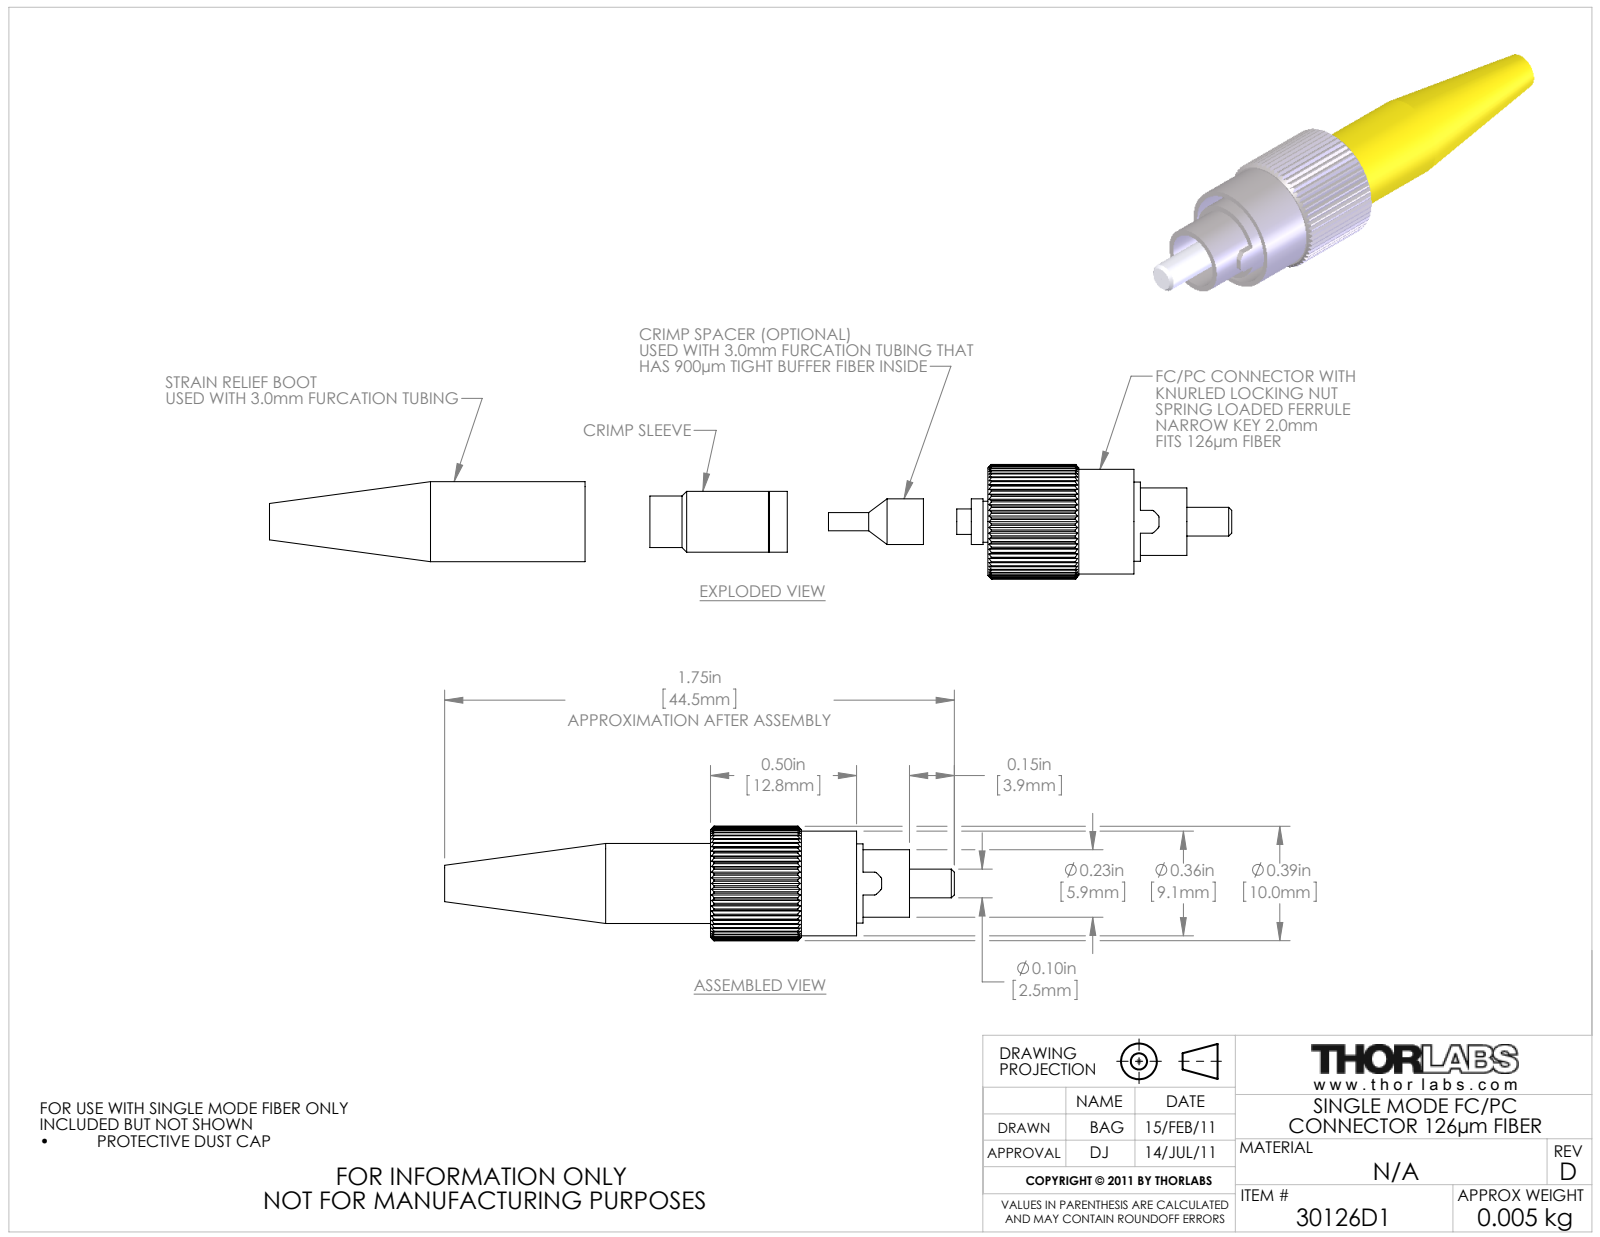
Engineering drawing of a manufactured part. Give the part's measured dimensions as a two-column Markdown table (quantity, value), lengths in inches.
| quantity | value |
| --- | --- |
| part name | 1065-E0W |
| STEP written by | SolidWorks 2011 (AUTOMOTIVE_DESIGN) |
| units | inches |
| bodies | 5 solids, 303 faces (155 planar, 126 cylindrical, 22 other) |
| overall size | 1.752 × 0.393 × 0.393 |
| volume | 0.073 in³ |
| surface area | 4.548 in² |
| round holes (diameter × count) | 0.045 × 1, 0.056 × 1, 0.127 × 1, 0.13 × 1, 0.172 × 1, 0.192 × 1, 0.205 × 1, 0.25 × 1, 0.325 × 1, 0.36 × 1 |
| round bosses / shafts (diameter × count) | 0.275 × 1, 0.272 × 1, 0.232 × 1, 0.209 × 1, 0.19 × 1, 0.177 × 1, 0.157 × 1, 0.141 × 1 |
| partial cylindrical surfaces (radius × count) | 0.008 × 4, 0.197 × 1 |
| main face-to-face distances | 0.267, 0.023, 0.022, 0.121, 0.098, 0.331, 0.045, 0.143, 0.387, 0.365 |
